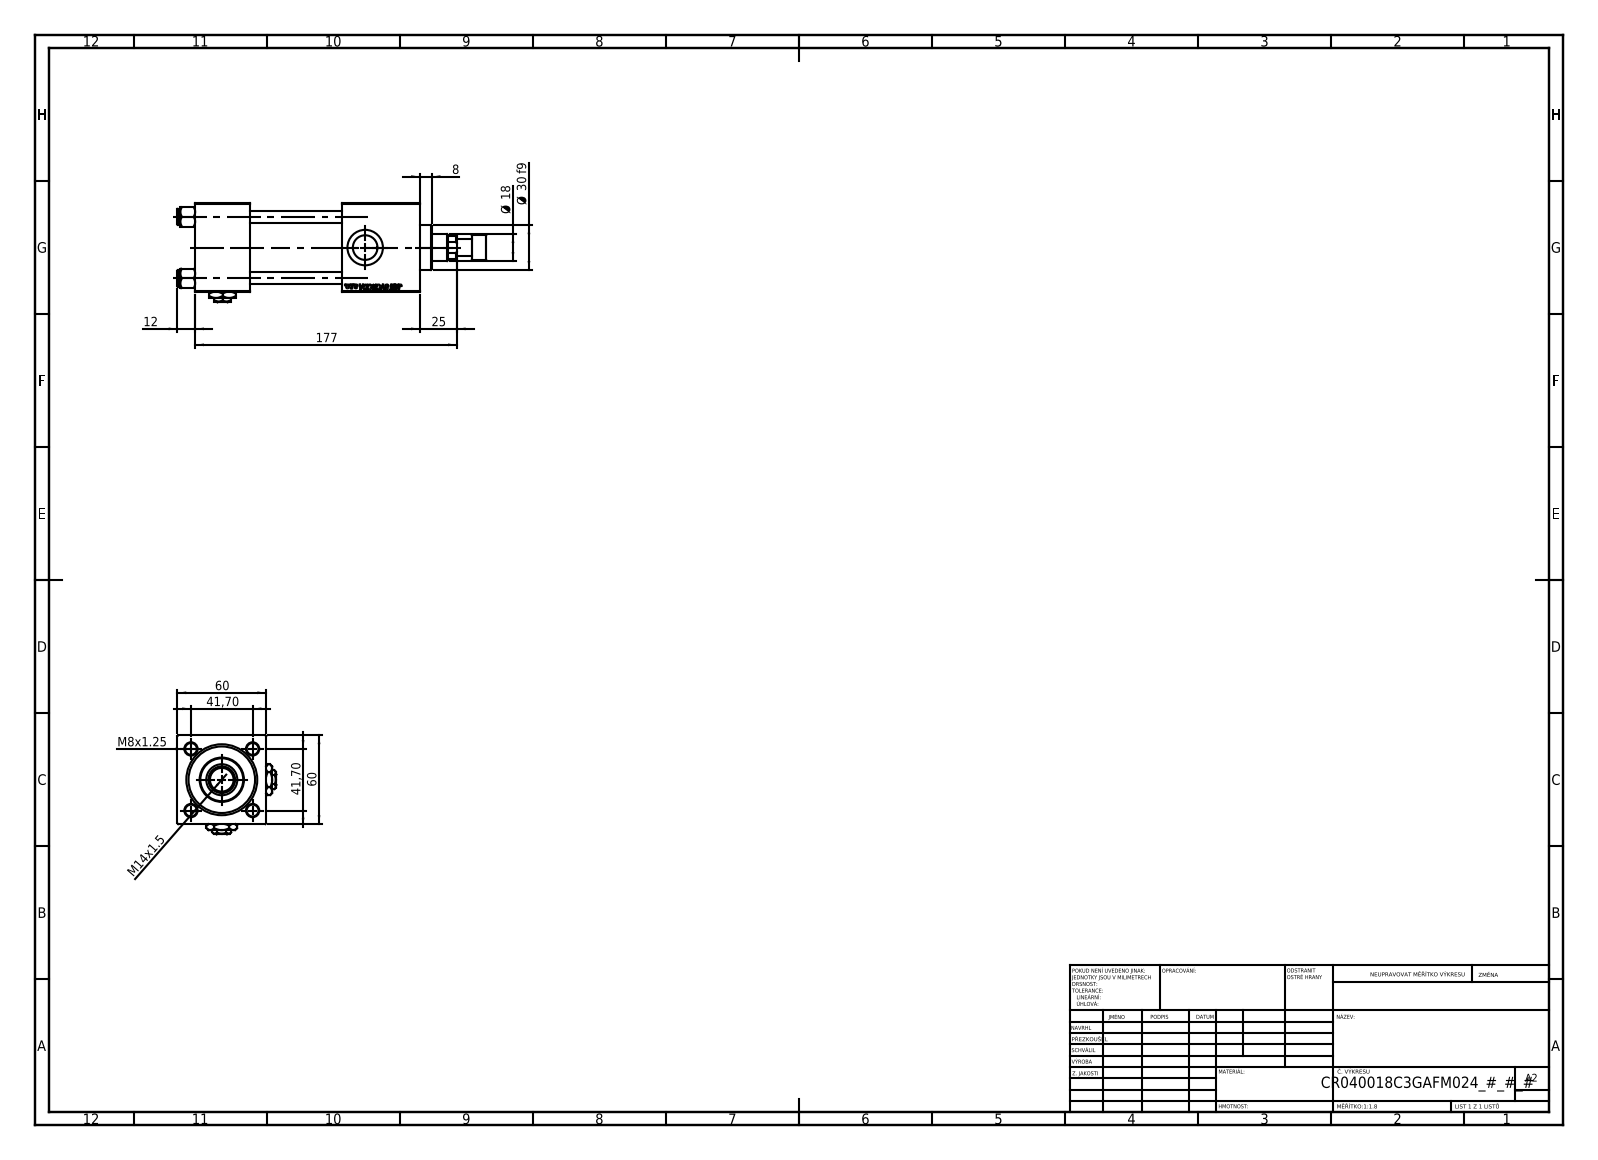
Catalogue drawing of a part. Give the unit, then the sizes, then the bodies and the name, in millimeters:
Units: millimetres
Overall size (bounding box): 209 × 67 × 67
Round holes (diameter × count): ⌀8 ×4, ⌀7 ×2, ⌀16.66 ×2, ⌀24 ×2, ⌀8.5 ×1, ⌀18 ×1, ⌀21 ×1, ⌀31 ×1, ⌀40 ×1, ⌀45 ×1
Round bosses / shafts (diameter × count): ⌀11 ×5, ⌀46 ×1, ⌀30 ×1, ⌀17 ×1
Main face-to-face distances: 60, 37, 152, 115, 53, 62, 99, 123.3, 86.3, 24.3
Hole centre spacings: 29.49, 41.7, 58.97
Volume: 405 499 mm³ · Surface area: 111 355 mm²
Bodies: 14 solids, 1261 faces (577 planar, 102 cylindrical, 582 other)
Part name (STEP PRODUCT): V215_VC_A; V215CR_C_Body; Zatka_pro_OIL_PORT; V215CR_C_TYCINKA (+3 more)
STEP written by: SolidWorks 2019 (CONFIG_CONTROL_DESIGN)
